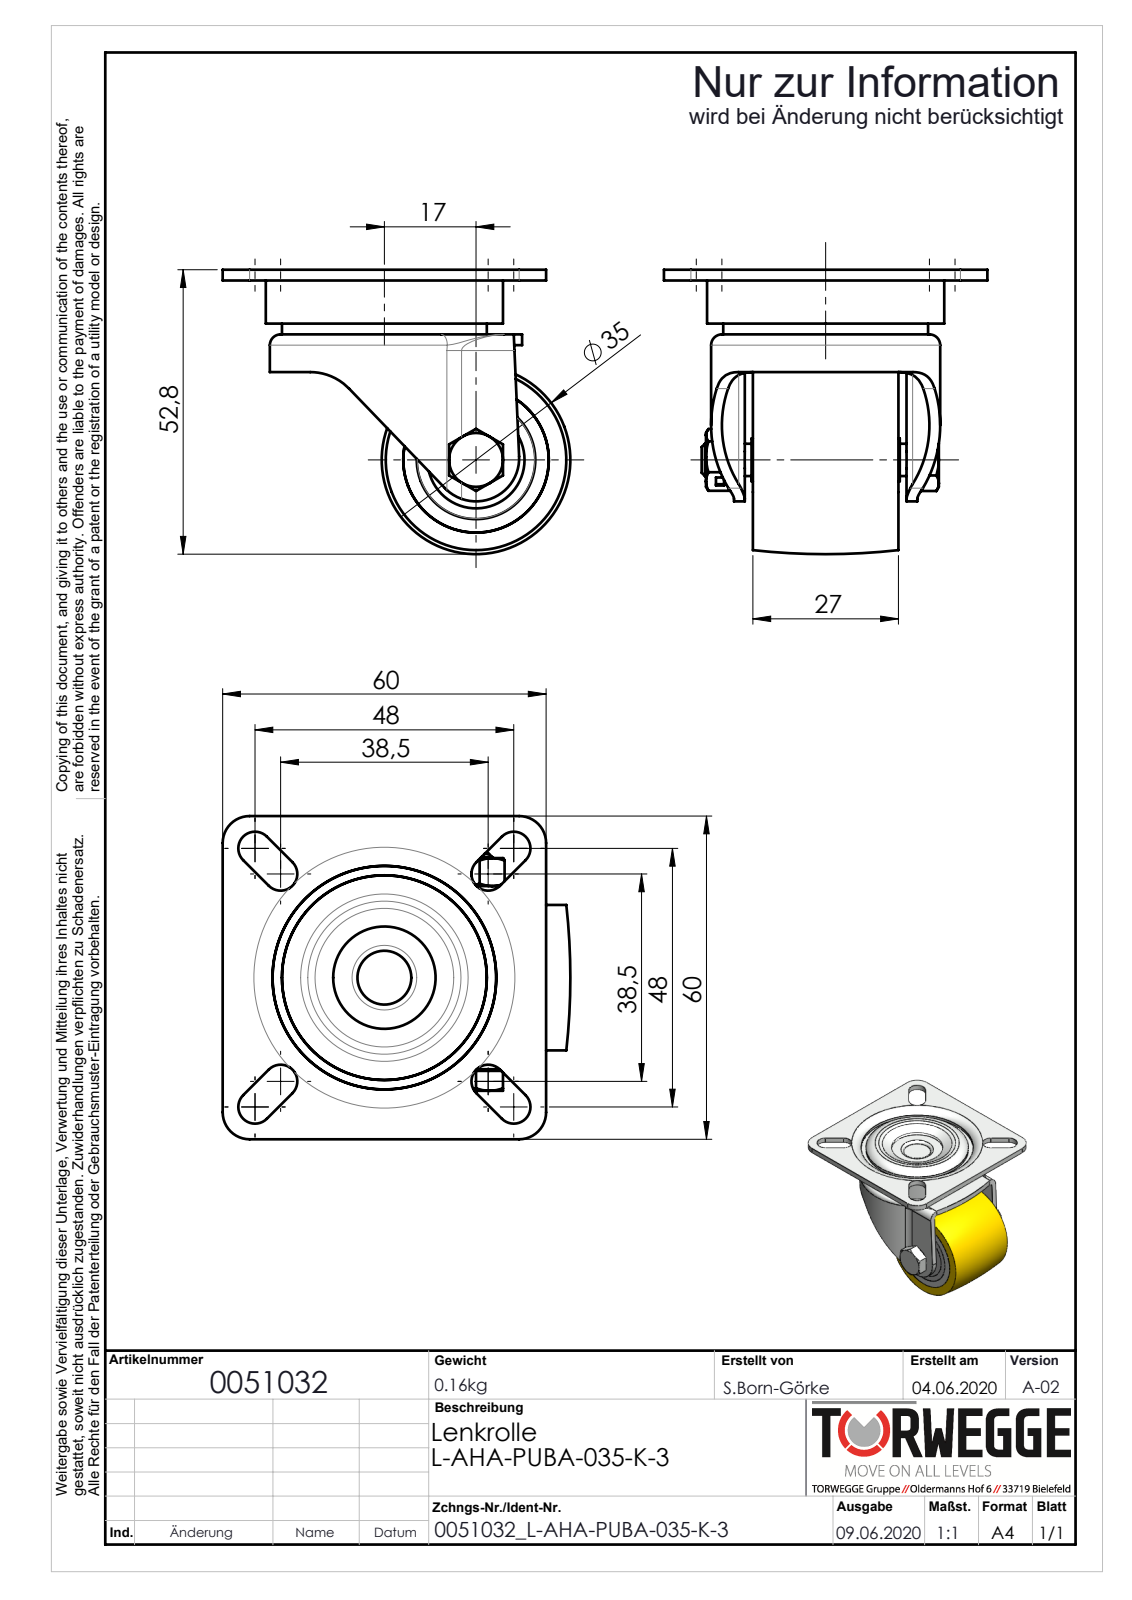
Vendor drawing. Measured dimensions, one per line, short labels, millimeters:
name: 0051032
written by: SolidWorks 2018 (AUTOMOTIVE_DESIGN)
unit: mm
bodies: 19 solids, 304 faces (98 planar, 114 cylindrical, 92 other)
size: 64.5 × 60 × 52.8
volume: 36 901 mm³; area: 37 657 mm²
holes: 1× ⌀5, 1× ⌀6, 1× ⌀6.2, 1× ⌀8, 1× ⌀8.6, 1× ⌀18, 1× ⌀27, 1× ⌀34, 1× ⌀40, 1× ⌀41.5
bosses: 1× ⌀44, 1× ⌀38, 1× ⌀23, 1× ⌀22, 1× ⌀12, 1× ⌀10, 1× ⌀7.95
rounds: 8× R3.1, 6× R5, 2× R1, 2× R3, 2× R7, 1× R8, 1× R10, 1× R19.25
face distances: 2, 4, 10, 5, 1, 6, 7, 3, 20, 8
